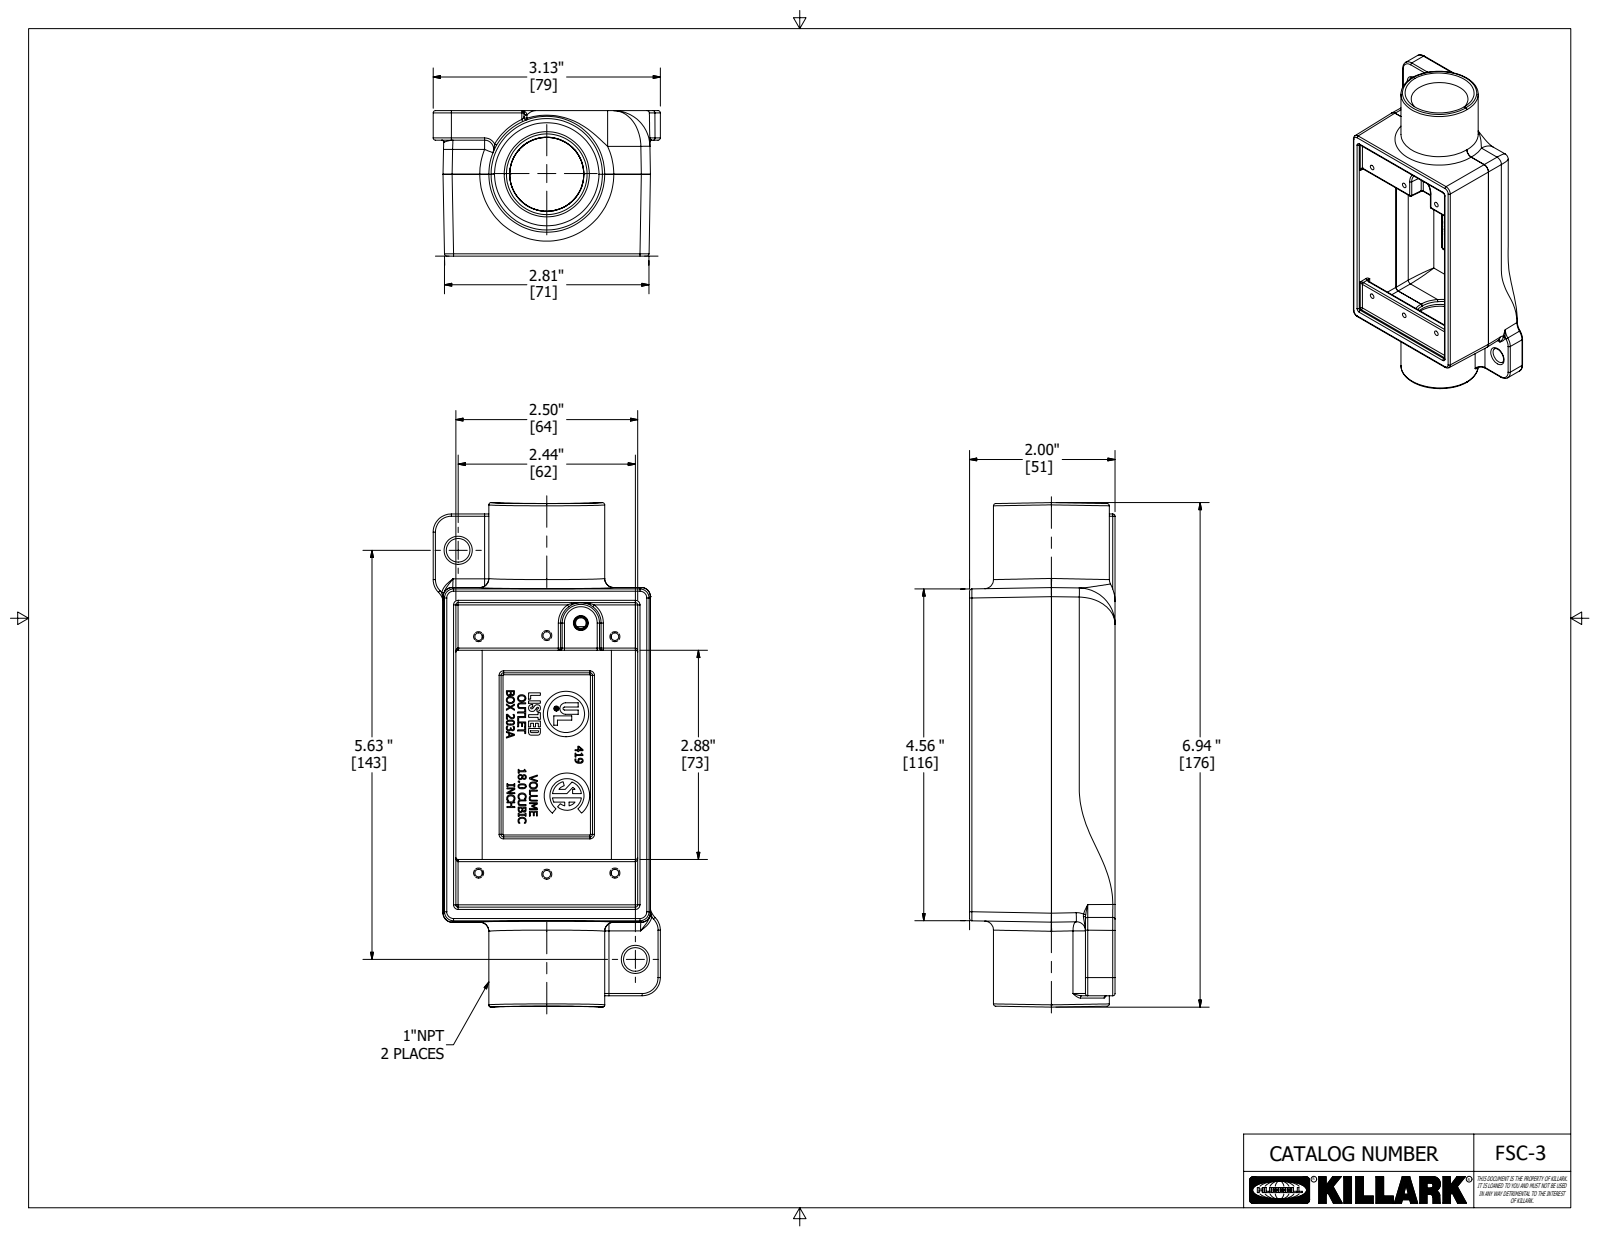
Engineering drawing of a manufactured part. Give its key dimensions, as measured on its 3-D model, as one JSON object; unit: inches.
{"part_name": "23643-3", "step_written_by": "Autodesk Inventor 2020 (AUTOMOTIVE_DESIGN)", "units": "inches", "bodies": {"solids": 1, "faces": 1238, "planar": 568, "cylindrical": 183, "other": 487}, "overall_size": [6.937, 3.125, 2], "volume_in3": 9.537, "surface_area_in2": 104.4, "round_holes": [[0.104, 6], [0.069, 1], [0.145, 1], [0.625, 1]], "round_bosses_or_shafts": [[1.594, 1], [0.509, 1], [0.058, 1]], "partial_cylinders_radius": [[0.031, 67], [0.062, 15], [0.125, 14], [0.094, 7], [0.375, 4], [0.013, 2], [0.014, 2], [0.034, 2]], "face_to_face_distances": [0.156, 2.695, 1.75, 2.851, 1.594, 0.031, 1.719, 2.539, 1.906, 0.25], "hole_center_spacings": [0.937, 3.397, 1.875, 3.25, 3.752, 0.153, 0.5, 0.505]}
